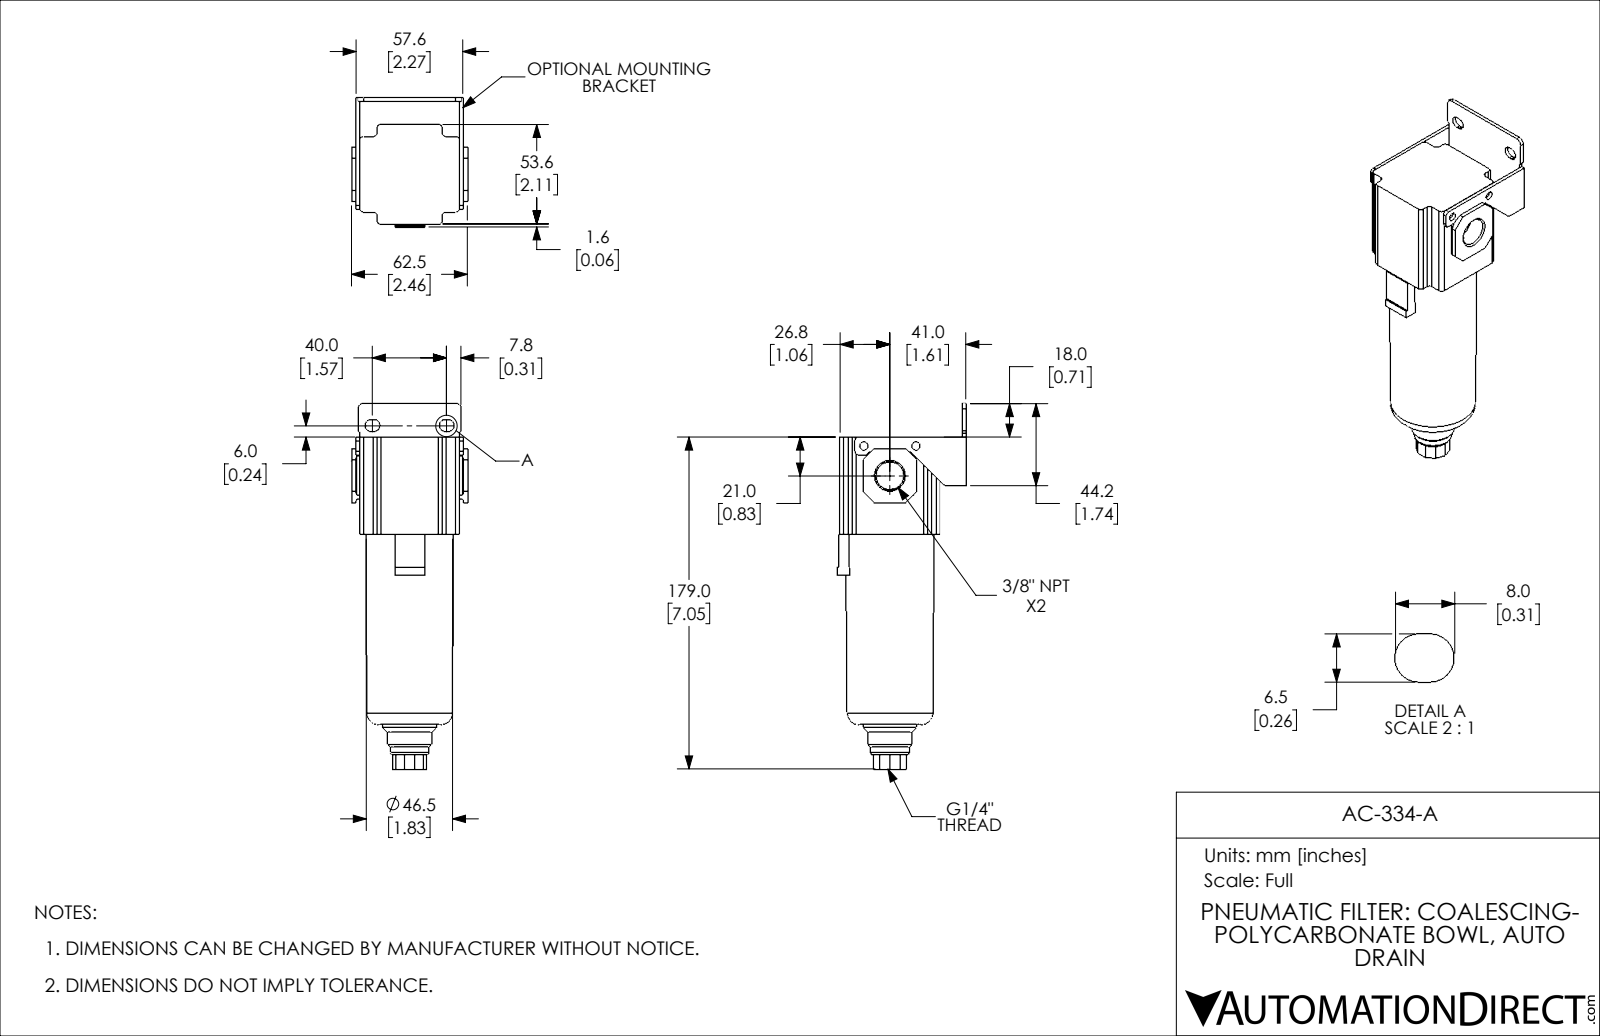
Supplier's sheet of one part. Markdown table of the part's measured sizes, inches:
| quantity | value |
| --- | --- |
| part name | AC-334-A |
| STEP written by | SolidWorks 2018 (AUTOMOTIVE_DESIGN) |
| units | inches |
| bodies | 1 solid, 173 faces (109 planar, 48 cylindrical, 16 other) |
| overall size | 7.756 × 2.733 × 2.461 |
| volume | 19.92 in³ |
| surface area | 65.58 in² |
| round holes (diameter × count) | 0.177 × 2, 0.451 × 1, 0.589 × 1 |
| round bosses / shafts (diameter × count) | 1.102 × 1, 0.906 × 1, 0.787 × 1 |
| partial cylindrical surfaces (radius × count) | 0.079 × 15, 0.128 × 4, 0.039 × 2, 0.118 × 2 |
| main face-to-face distances | 0.079, 2.11, 2.189, 0.559, 2.669, 0.48, 2.591, 2.067, 0.258, 1.852 |
| hole center spacings | 0.837, 1.102 |
